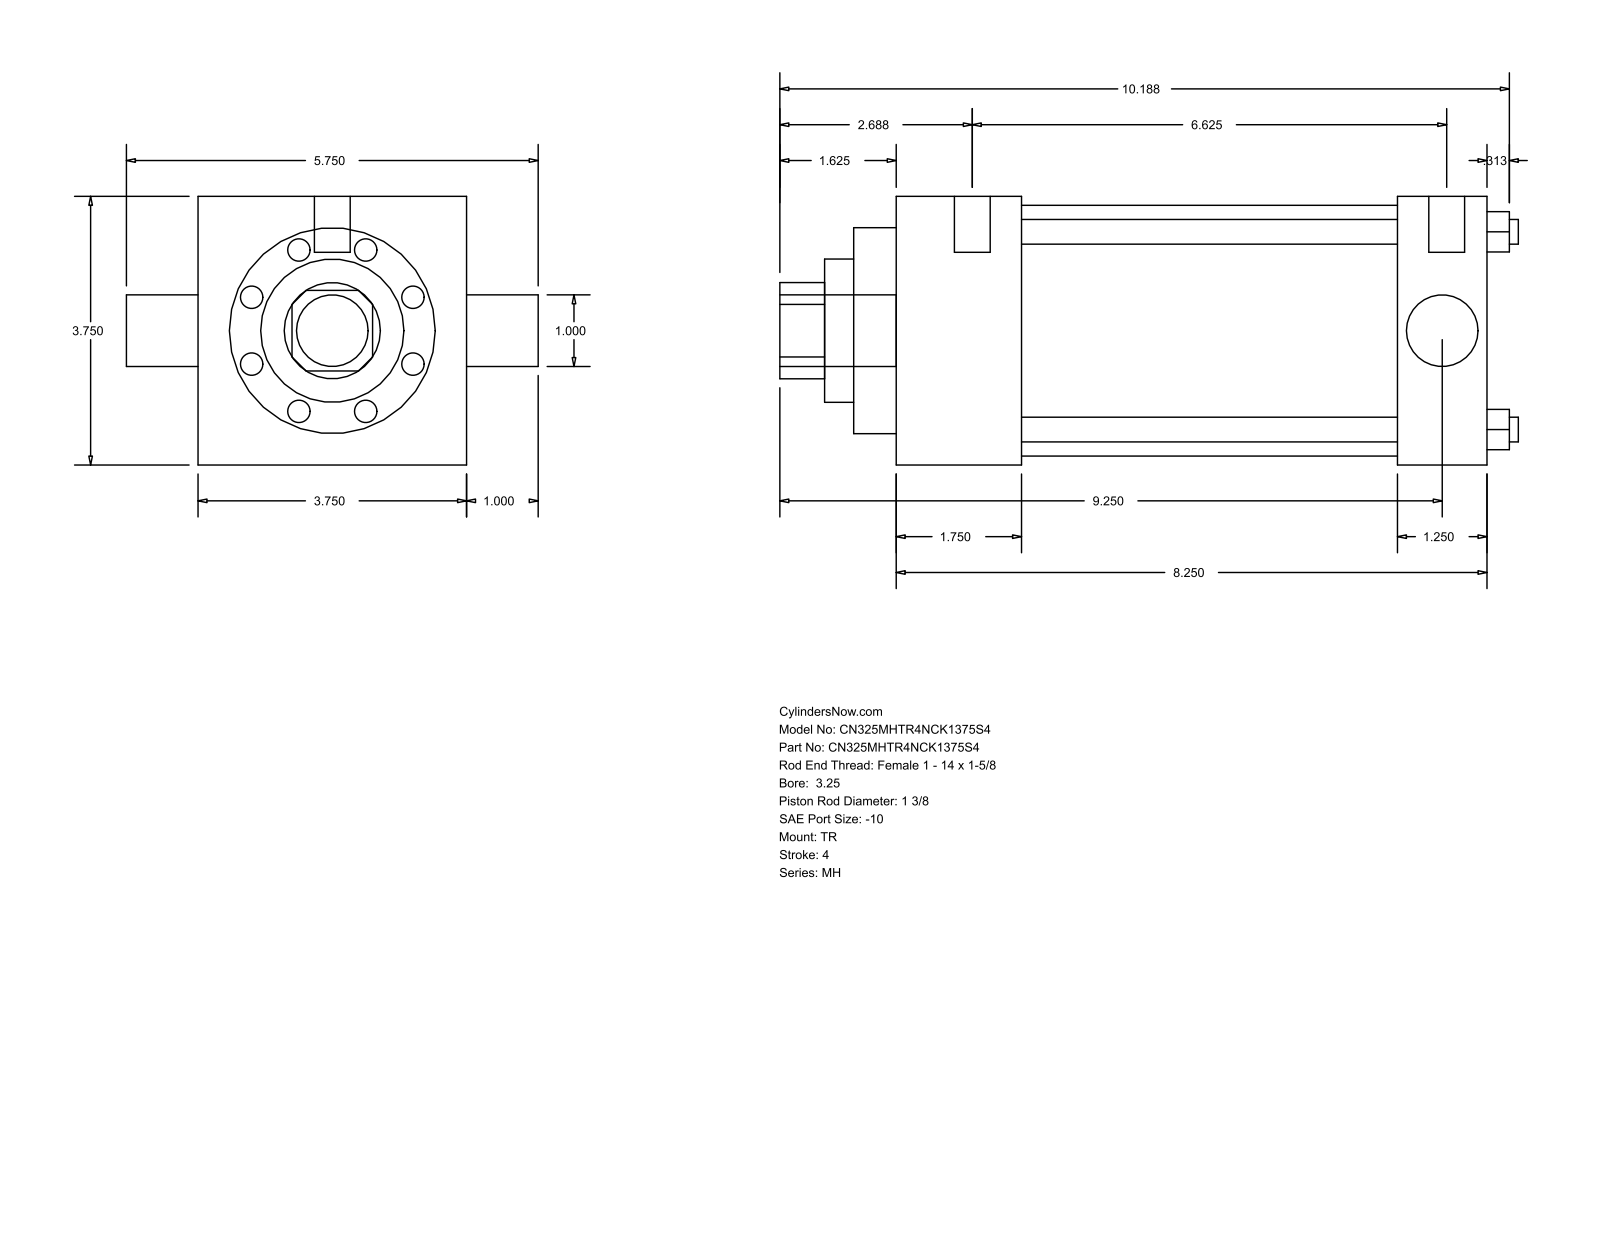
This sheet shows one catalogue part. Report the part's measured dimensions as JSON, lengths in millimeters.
{"part_name": "MH_TR__0325_1.375", "step_written_by": "GSSL Pune (CONFIG_CONTROL_DESIGN)", "units": "millimeters", "bodies": {"solids": 0, "faces": 86, "planar": 61, "cylindrical": 25, "other": 0}, "overall_size": [261.94, 146.05, 95.25], "round_holes": [[8.76, 4], [25.4, 1], [34.92, 1], [50.8, 1], [73.03, 1], [88.9, 1]], "round_bosses_or_shafts": [[5.56, 3], [12.7, 2], [25.4, 1]], "partial_cylinders_radius": [[17.06, 1]], "face_to_face_distances": [95.24, 209.55, 44.45, 177.8, 133.35, 165.1, 31.75, 15.08, 59.53, 192.88], "hole_center_spacings": [49.57, 70.1, 99.14]}
